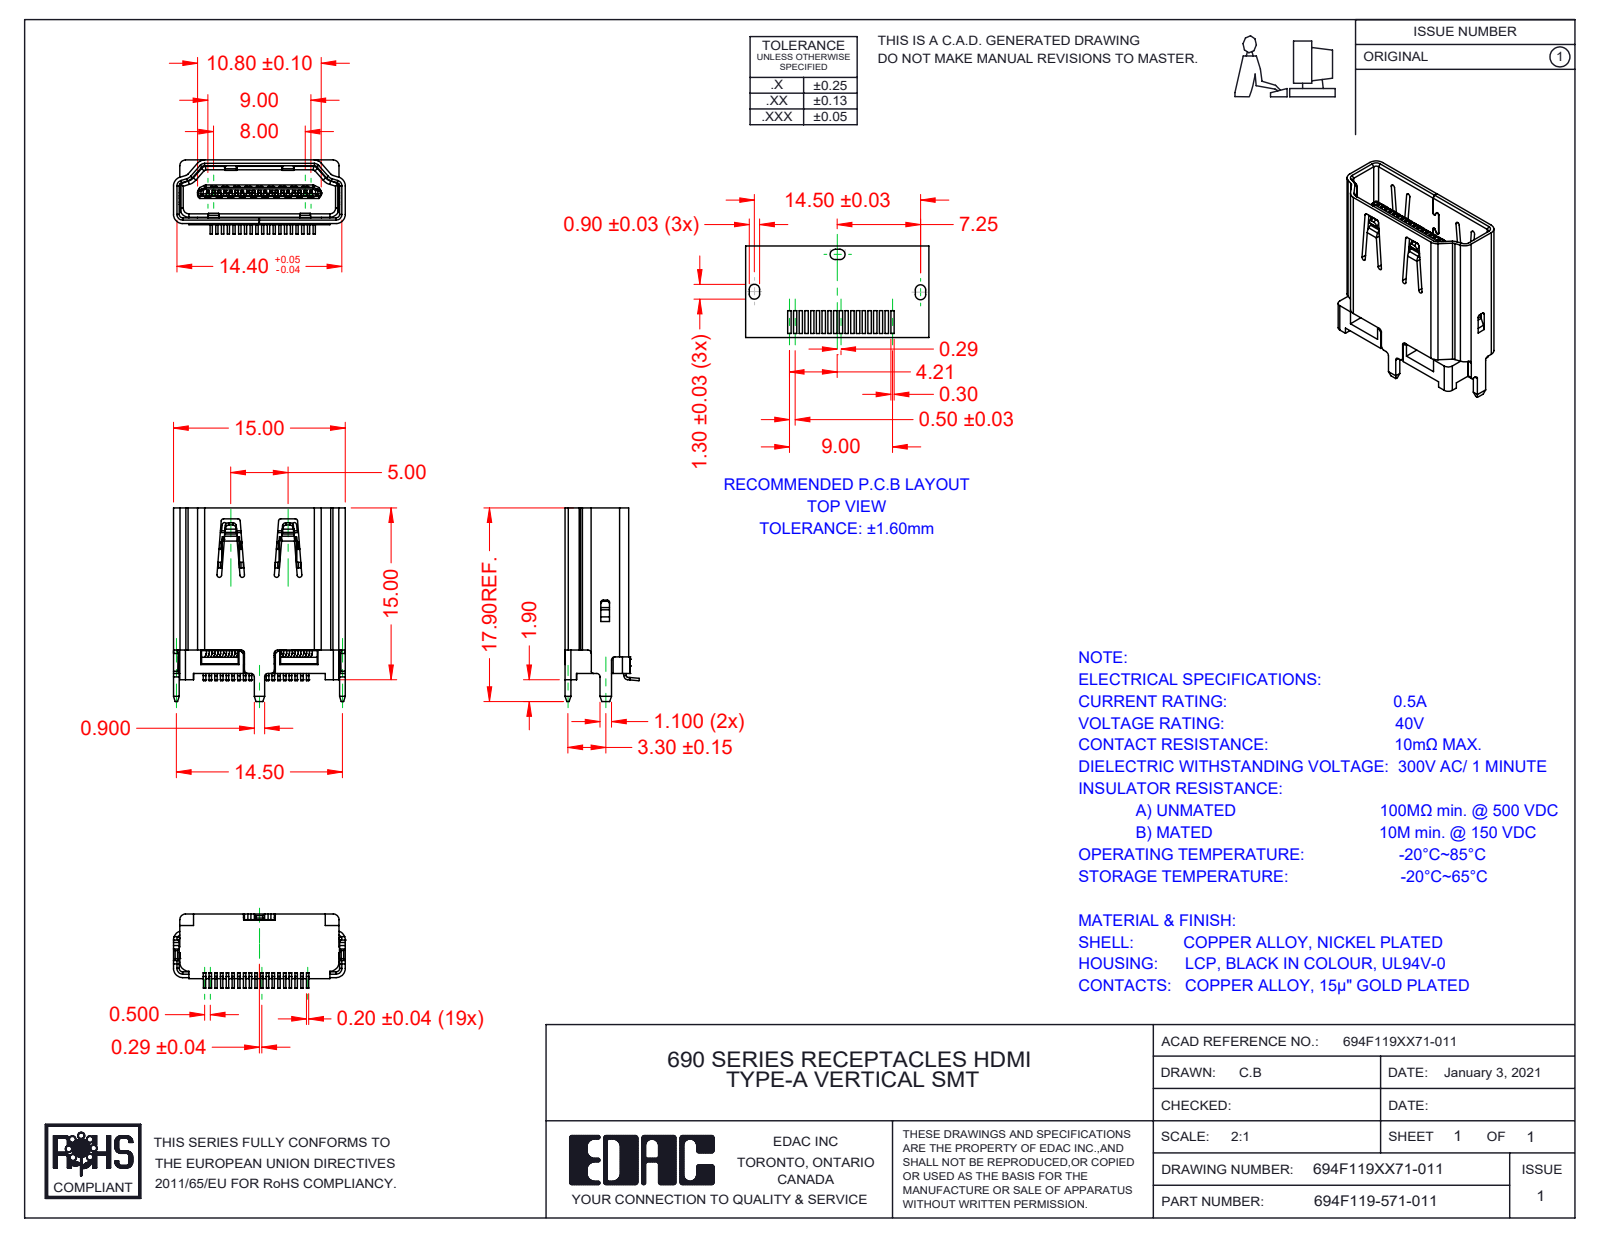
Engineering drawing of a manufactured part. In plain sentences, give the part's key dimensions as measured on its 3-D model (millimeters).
The part is named "Insulator 694F119XX71-011; 694F119-171-011; Shell 694F119XX71-011; Contacts 694F119XX71-011". Its 3-D file was written by "SolidWorks 2020 (AUTOMOTIVE_DESIGN)". It is 21 solids with 3937 faces: 2871 planar, 984 cylindrical and 82 other. Overall it measures 16.9 by 15 by 6.47 millimeters. Its volume is 556 cubic millimeters and its surface area 2 337 square millimeters. Partial cylindrical surfaces (rounded edges, fillets, slot ends): 61 of radius 0.3, 42 of radius 0.1, 40 of radius 0.2, 38 of radius 0.54, 35 of radius 0.15, 12 of radius 0.35, 8 of radius 0.8, 6 of radius 0.5. The main face-to-face distances are 0.5, 5.05, 5.55, 4.55, 0.55, 0.7, 2.52, 2.53, 0.35, 1.
